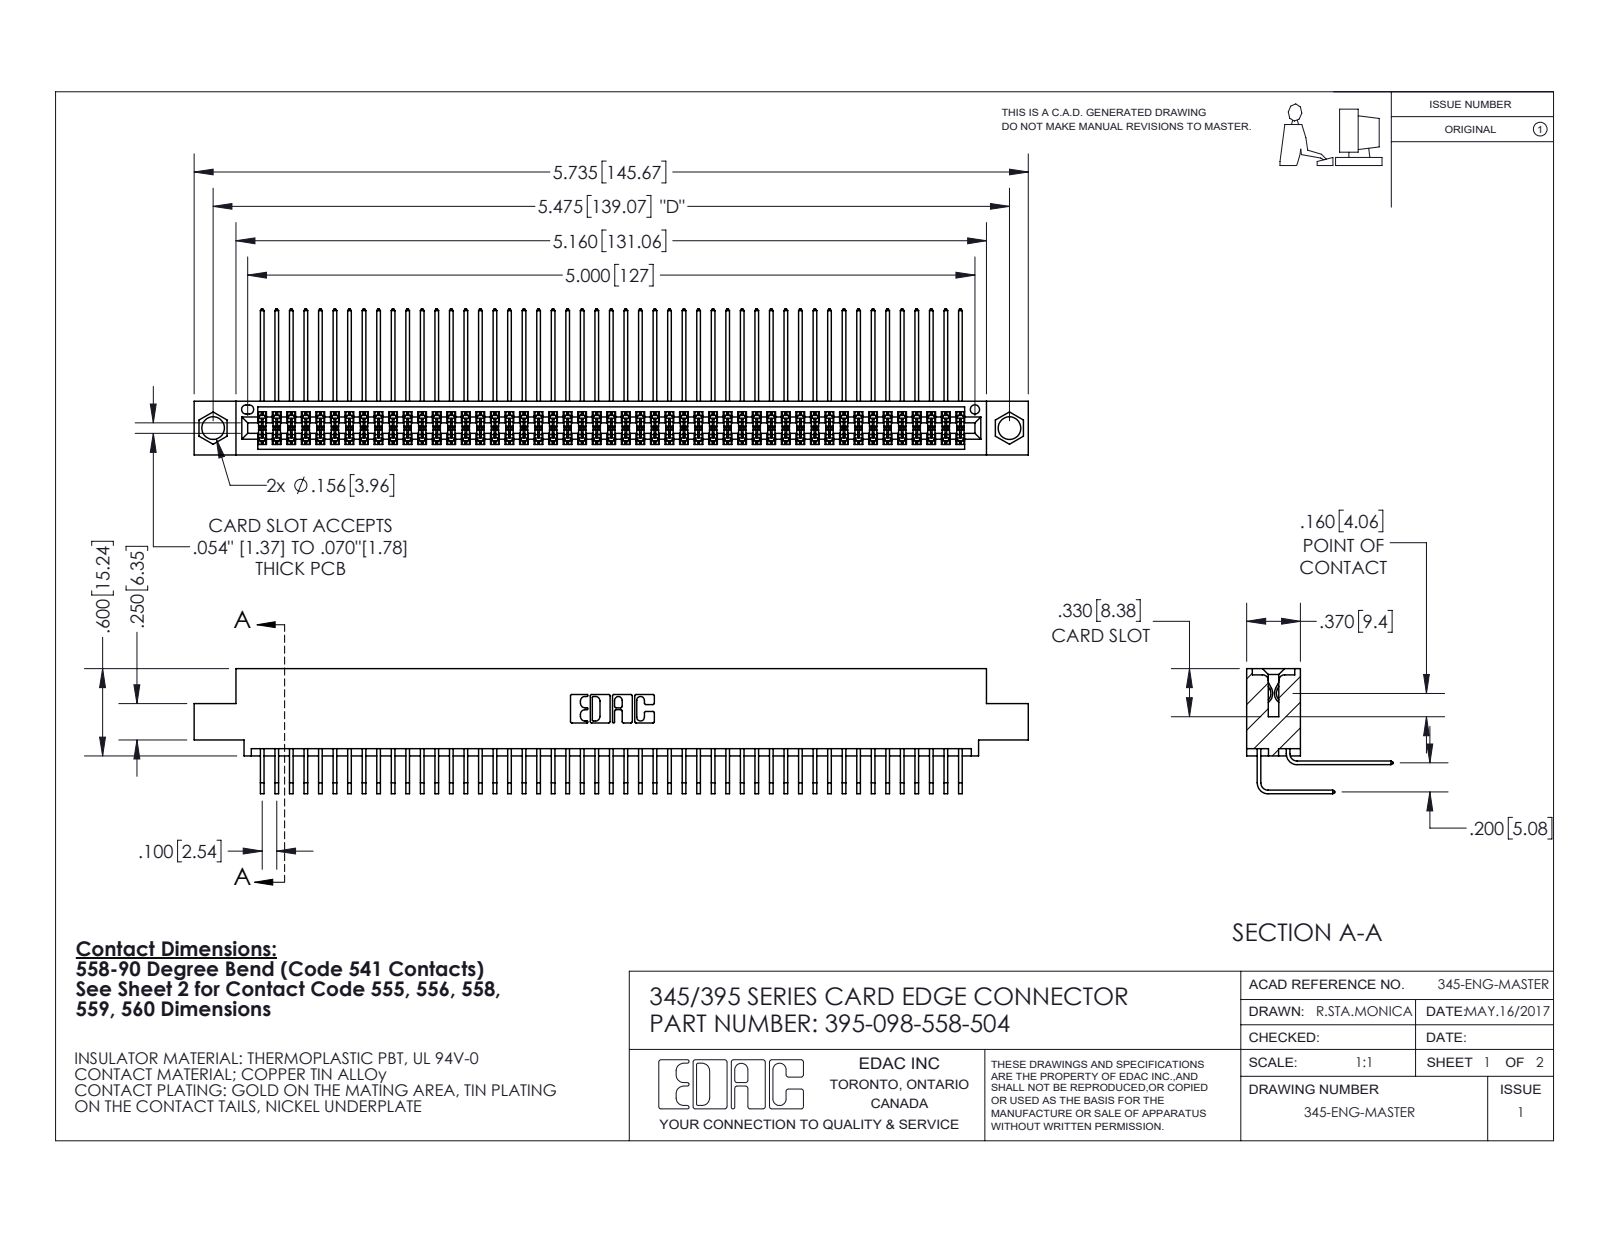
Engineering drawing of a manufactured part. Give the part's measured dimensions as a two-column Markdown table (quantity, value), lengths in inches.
| quantity | value |
| --- | --- |
| part name | 345-292-001_558 559 Tail - 1; 395-098-558-504; 345-292-001_558 Tail - 2; 345 Part_0.110 Offset - 0.156 Dia-TI |
| STEP written by | SolidWorks 2020 (CONFIG_CONTROL_DESIGN) |
| units | inches |
| bodies | 99 solids, 5240 faces (3528 planar, 1712 cylindrical, 0 other) |
| overall size | 5.735 × 1.005 × 0.859 |
| volume | 0.891 in³ |
| surface area | 37.7 in² |
| round holes (diameter × count) | 0.156 × 2, 0.064 × 1 |
| partial cylindrical surfaces (radius × count) | 0.006 × 196, 0.01 × 22, 0.007 × 6, 0.031 × 6, 0.026 × 3, 0.014 × 2, 0.019 × 2, 0.022 × 2 |
| main face-to-face distances | 0.072, 0.298, 0.2, 0.37, 0.098, 0.272, 0.025, 0.225, 0.025, 0.175 |
| hole center spacings | 0.27, 5.239, 5.475 |
